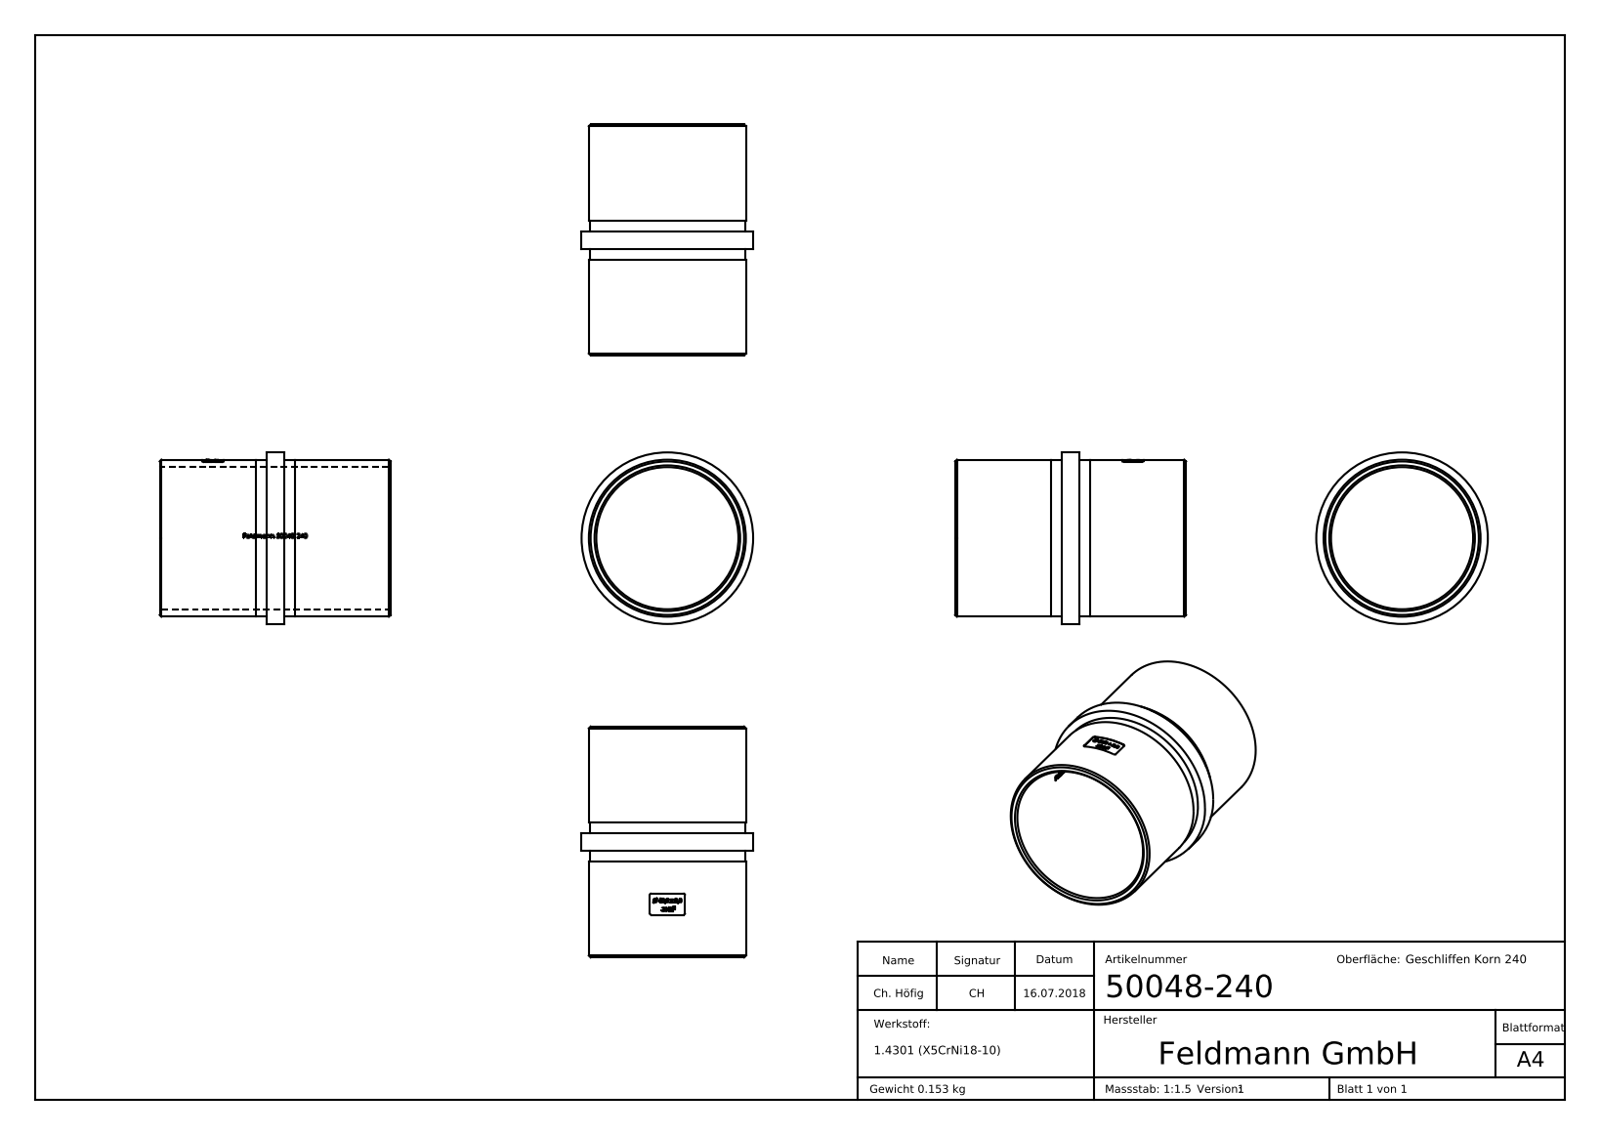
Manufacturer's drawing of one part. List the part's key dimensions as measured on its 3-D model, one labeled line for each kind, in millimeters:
Part name (STEP PRODUCT): 50048-240
STEP written by: SolidWorks 2015 (CONFIG_CONTROL_DESIGN)
Units: millimetres
Bodies: 1 solid, 452 faces (185 planar, 71 cylindrical, 196 other)
Overall size (bounding box): 65 × 48.3 × 48.3
Volume: 19 304 mm³ · Surface area: 18 376 mm²
Round holes (diameter × count): ⌀40 ×1
Round bosses / shafts (diameter × count): ⌀48.3 ×1, ⌀44.2 ×1, ⌀43.8 ×1
Partial cylindrical surfaces — rounded edges, fillets, slot ends (radius × count): R0.5 ×4, R20.1 ×1, R22 ×1
Main face-to-face distances: 5, 30, 35, 65, 27, 38, 3, 8, 11, 12
